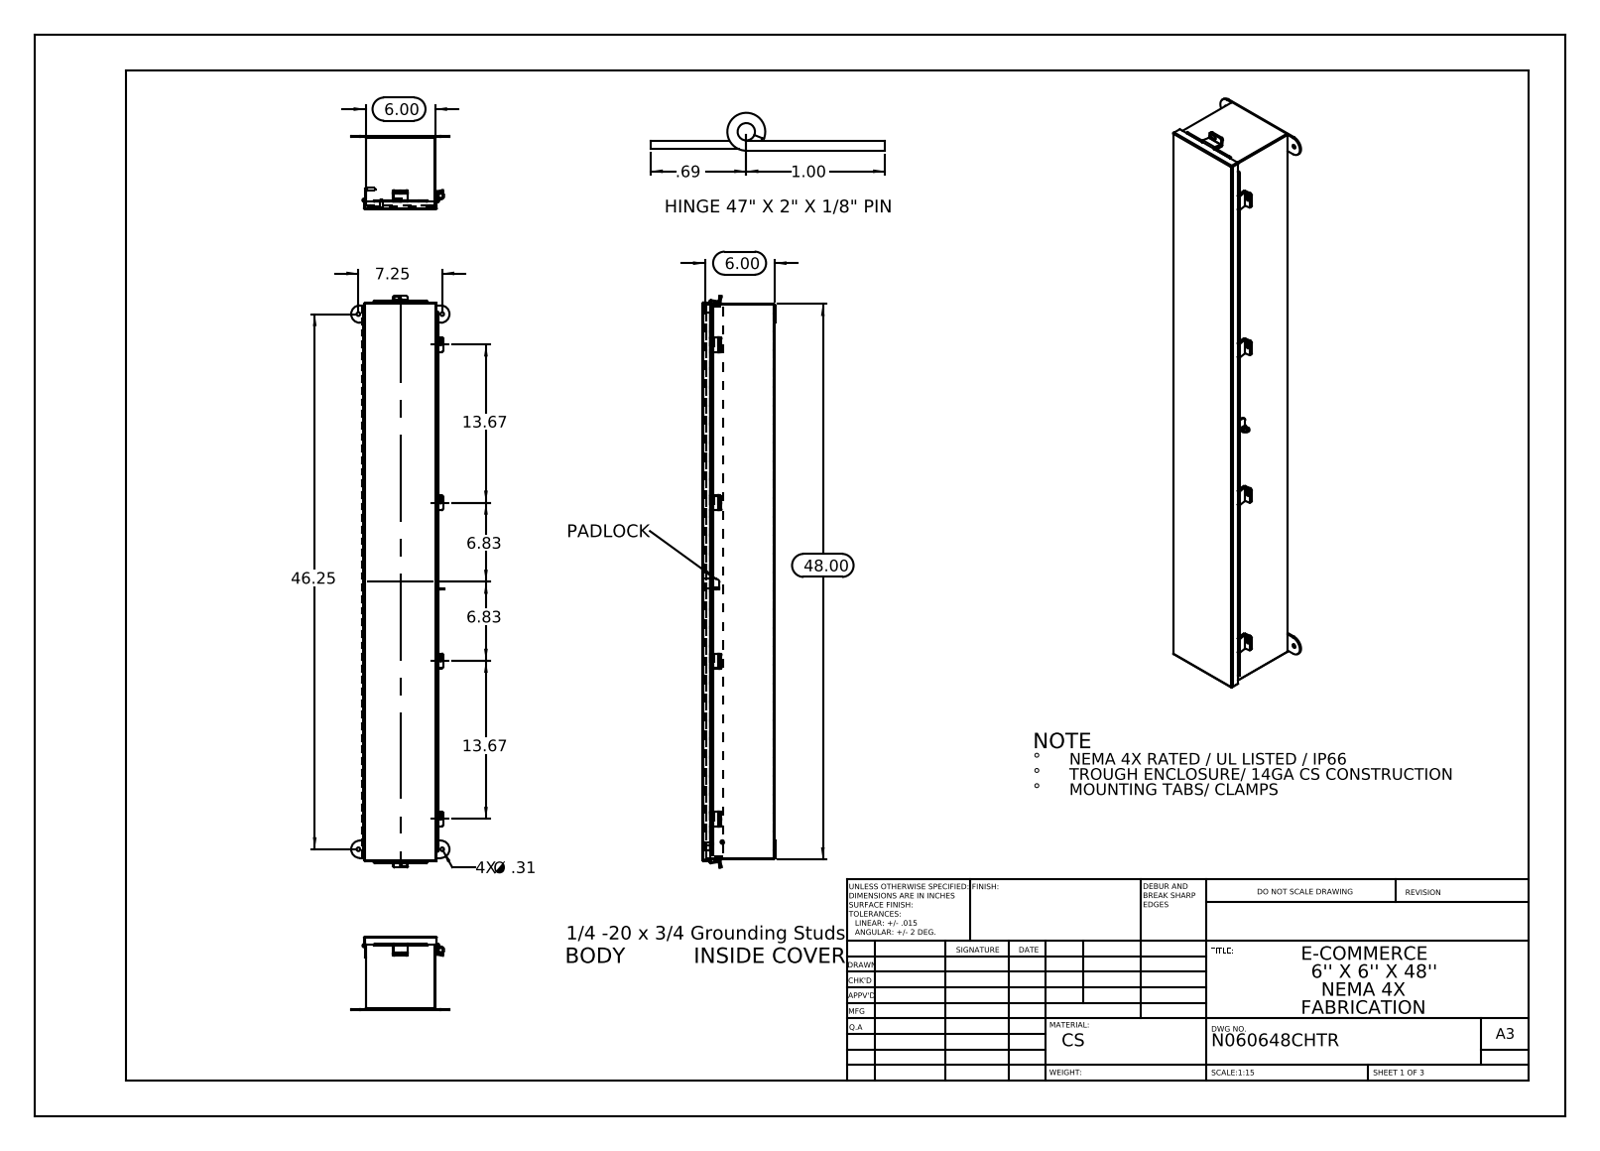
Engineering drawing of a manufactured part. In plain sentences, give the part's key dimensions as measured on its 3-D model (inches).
The part is named "HW-CLH-JH-20154; N060648SSCHTR JIC Clamp Bracket; N060648SSCHTR _JIC Hinge; N060648SSCHTR JIC Bottom (+8 more)". Its 3-D file was written by "SolidWorks 2013 (CONFIG_CONTROL_DESIGN)". It is 23 solids with 1376 faces: 825 planar, 531 cylindrical and 20 other. Overall it measures 49.407 by 8.5 by 6.337 inches. Its volume is 110.9 cubic inches and its surface area 2 994 square inches. Round holes: 6 of diameter 0.25, 4 of diameter 0.313, 1 of diameter 0.125, 1 of diameter 0.125, 1 of diameter 0.375. Round bosses or shafts: 2 of diameter 0.315, 2 of diameter 0.236, 1 of diameter 0.273, 1 of diameter 0.25. Partial cylindrical surfaces (rounded edges, fillets, slot ends): 24 of radius 0.125, 12 of radius 0.009, 12 of radius 0.133, 10 of radius 0.013, 10 of radius 0.088, 6 of radius 0.083, 6 of radius 0.1, 4 of radius 0.75. The main face-to-face distances are 0.075, 5.925, 6.128, 6, 5.85, 6.203, 6.053, 0.149, 6.074, 0.074. The hole center spacings are 7.25, 13.666, 27.332, 46.25, 46.815, 6.637, 13.666, 40.998.
